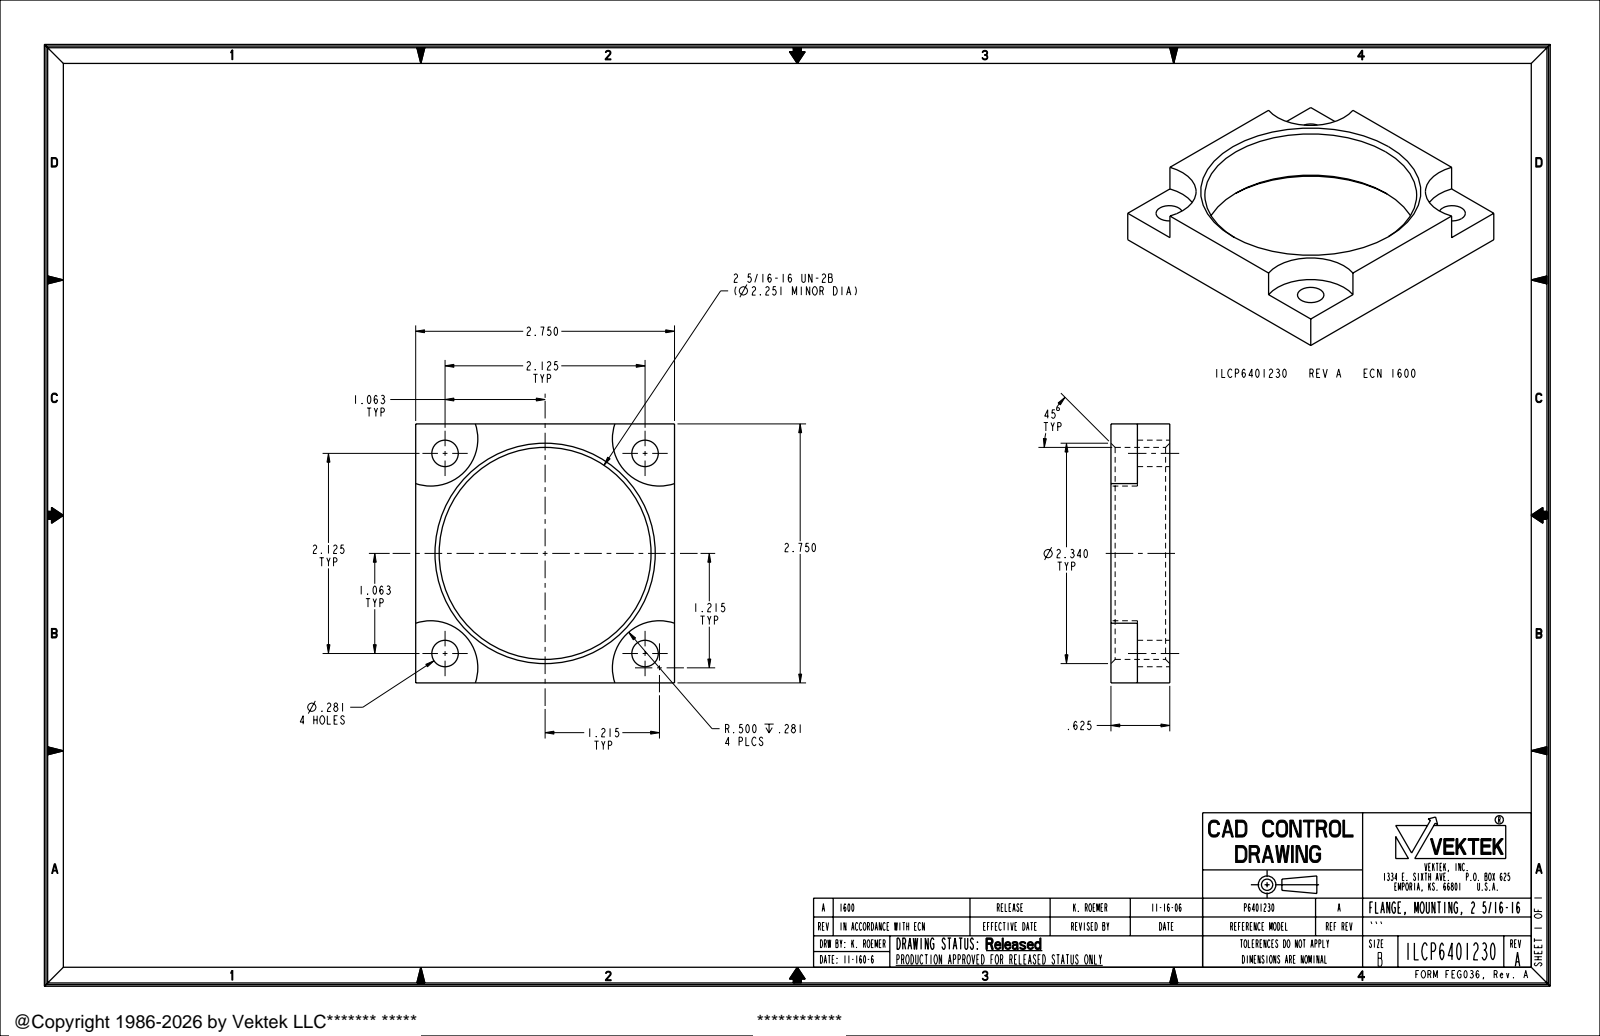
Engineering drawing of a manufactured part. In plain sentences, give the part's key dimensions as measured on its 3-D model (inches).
The part is named "ILCP6401230". Its 3-D file was written by "PRO/ENGINEER BY PARAMETRIC TECHNOLOGY CORPORATION, 2005180 (AUTOMOTIVE_DESIGN_CC2)". It is 1 solid with 28 faces: 10 planar, 14 cylindrical and 4 other. Overall it measures 2.75 by 2.75 by 0.625 inches. Its volume is 1.714 cubic inches and its surface area 18.64 square inches. Round holes: 4 of diameter 0.281, 1 of diameter 2.251. Partial cylindrical surfaces (rounded edges, fillets, slot ends): 4 of radius 0.5. The main face-to-face distances are 2.75, 0.625, 0.344, 0.281. The hole center spacings are 2.125, 1.502, 3.005, 1.502, 1.503.
